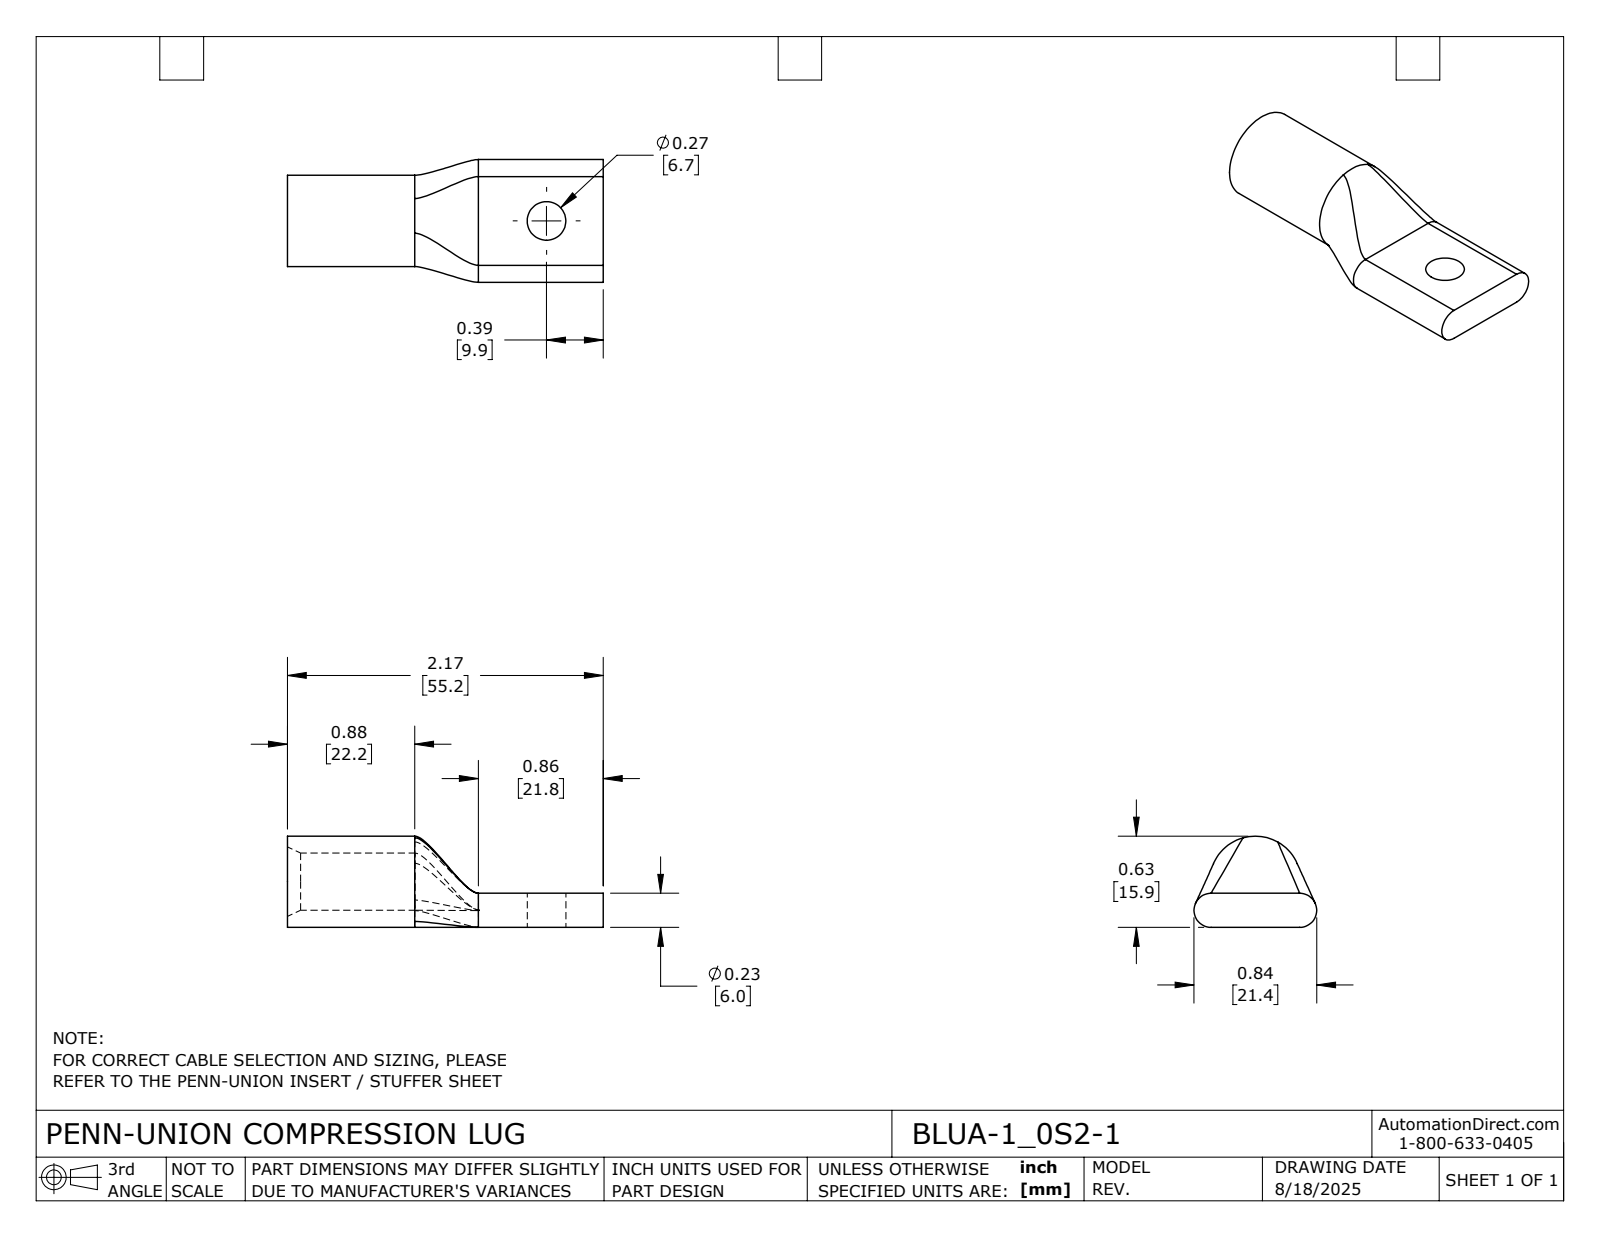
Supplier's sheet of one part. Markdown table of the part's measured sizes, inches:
| quantity | value |
| --- | --- |
| part name | BLUA-1_0S2-1 |
| STEP written by | SolidWorks 2024 (CONFIG_CONTROL_DESIGN) |
| units | inches |
| bodies | 1 solid, 24 faces (5 planar, 9 cylindrical, 10 other) |
| overall size | 2.172 × 0.844 × 0.627 |
| volume | 0.389 in³ |
| surface area | 6.453 in² |
| round holes (diameter × count) | 0.266 × 1, 0.393 × 1 |
| round bosses / shafts (diameter × count) | 0.627 × 1 |
| partial cylindrical surfaces (radius × count) | 0.117 × 2 |
| main face-to-face distances | 0.234, 2.172, 1.313, 0.859 |
